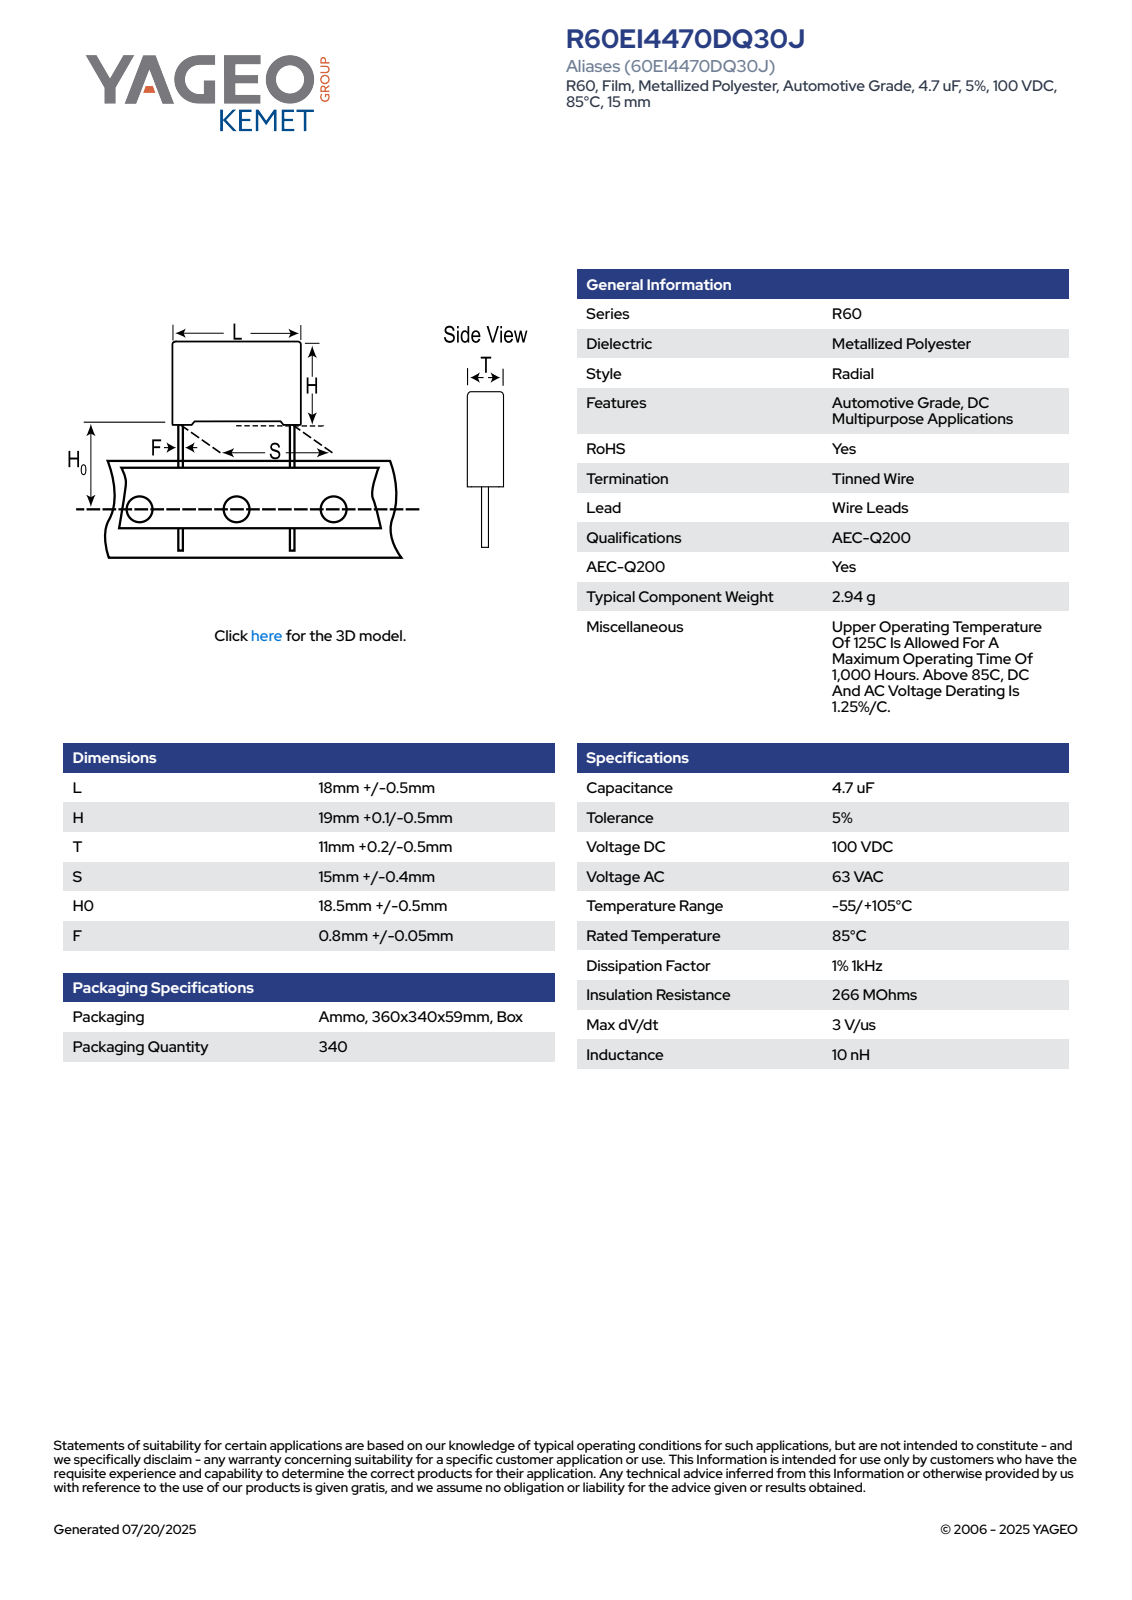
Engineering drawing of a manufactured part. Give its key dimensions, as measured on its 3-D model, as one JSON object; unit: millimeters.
{"part_name": "CFR_RB2_18X19X11_L18.5H19.1T11.2S15H019F0.85", "step_written_by": "SolidWorks 2020 (AUTOMOTIVE_DESIGN)", "units": "millimeters", "bodies": {"solids": 4, "faces": 85, "planar": 77, "cylindrical": 8, "other": 0}, "overall_size": [38.1, 18.5, 11.21], "volume_mm3": 3838, "surface_area_mm2": 1679, "round_bosses_or_shafts": [[0.85, 2]], "partial_cylinders_radius": [[0.5, 4]], "face_to_face_distances": [11.2, 18.5, 18.35, 0.62, 0.75, 19.1, 17.88, 0.66, 18.44, 10.58]}
